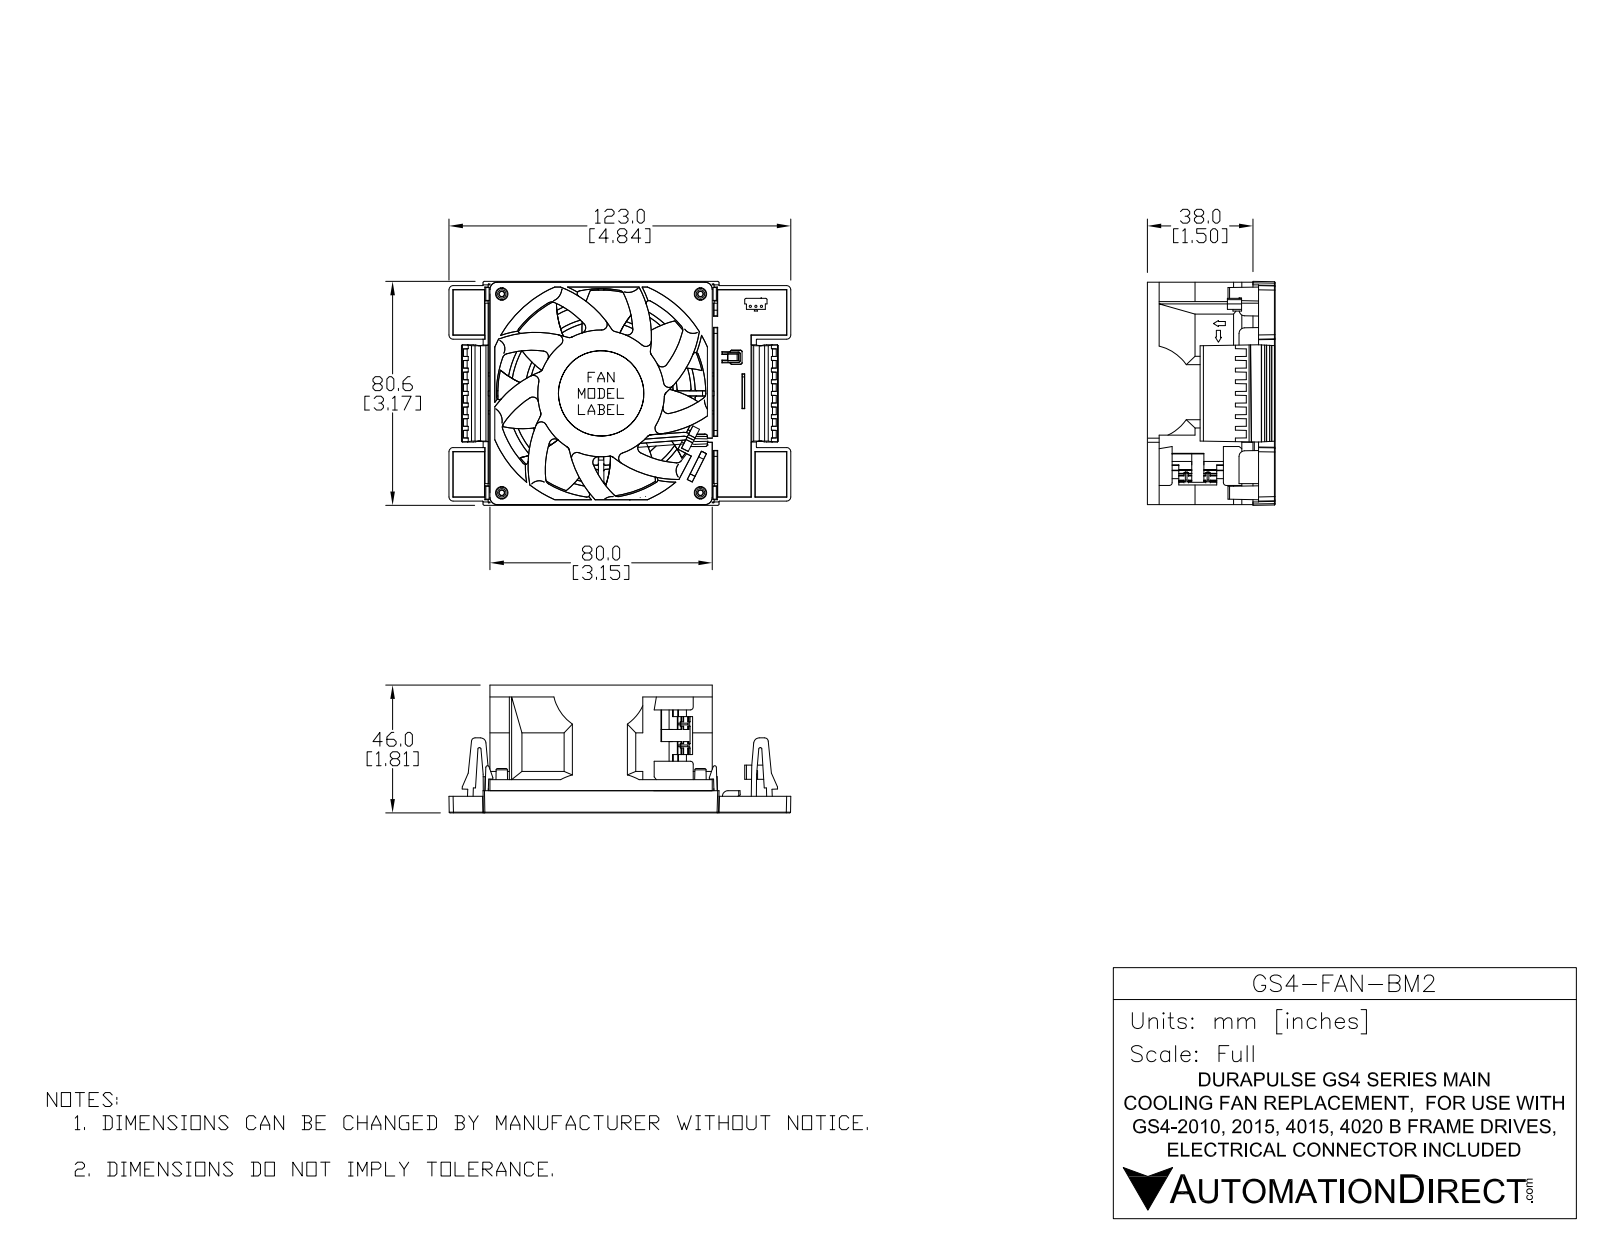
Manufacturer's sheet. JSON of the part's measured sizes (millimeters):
{"part_name": "GS4-FAN-BM2 GRILL b17b; GS4-FAN-BM2; GS4-FAN-BM2 FAN A New", "step_written_by": "SolidWorks 2016 (AUTOMOTIVE_DESIGN)", "units": "millimeters", "bodies": {"solids": 2, "faces": 821, "planar": 386, "cylindrical": 212, "other": 223}, "overall_size": [123, 80.6, 44], "volume_mm3": 100500, "surface_area_mm2": 68710, "round_holes": [[2.1, 4], [4.5, 4], [40.7, 1], [51.9, 1], [64.9, 1]], "round_bosses_or_shafts": [[54.8, 1], [45.8, 1], [41.1, 1]], "partial_cylinders_radius": [[0.3, 24], [0.4, 19], [5, 9], [0.4, 6], [0.5, 4], [0.5, 4], [0.5, 4], [0.6, 4]], "face_to_face_distances": [1, 77.8, 2, 4, 76.8, 6, 38, 78.8, 42, 44], "hole_center_spacings": [71.5, 101.1, 50.4, 50.5, 50.5, 50.5, 50.6, 50.6]}
